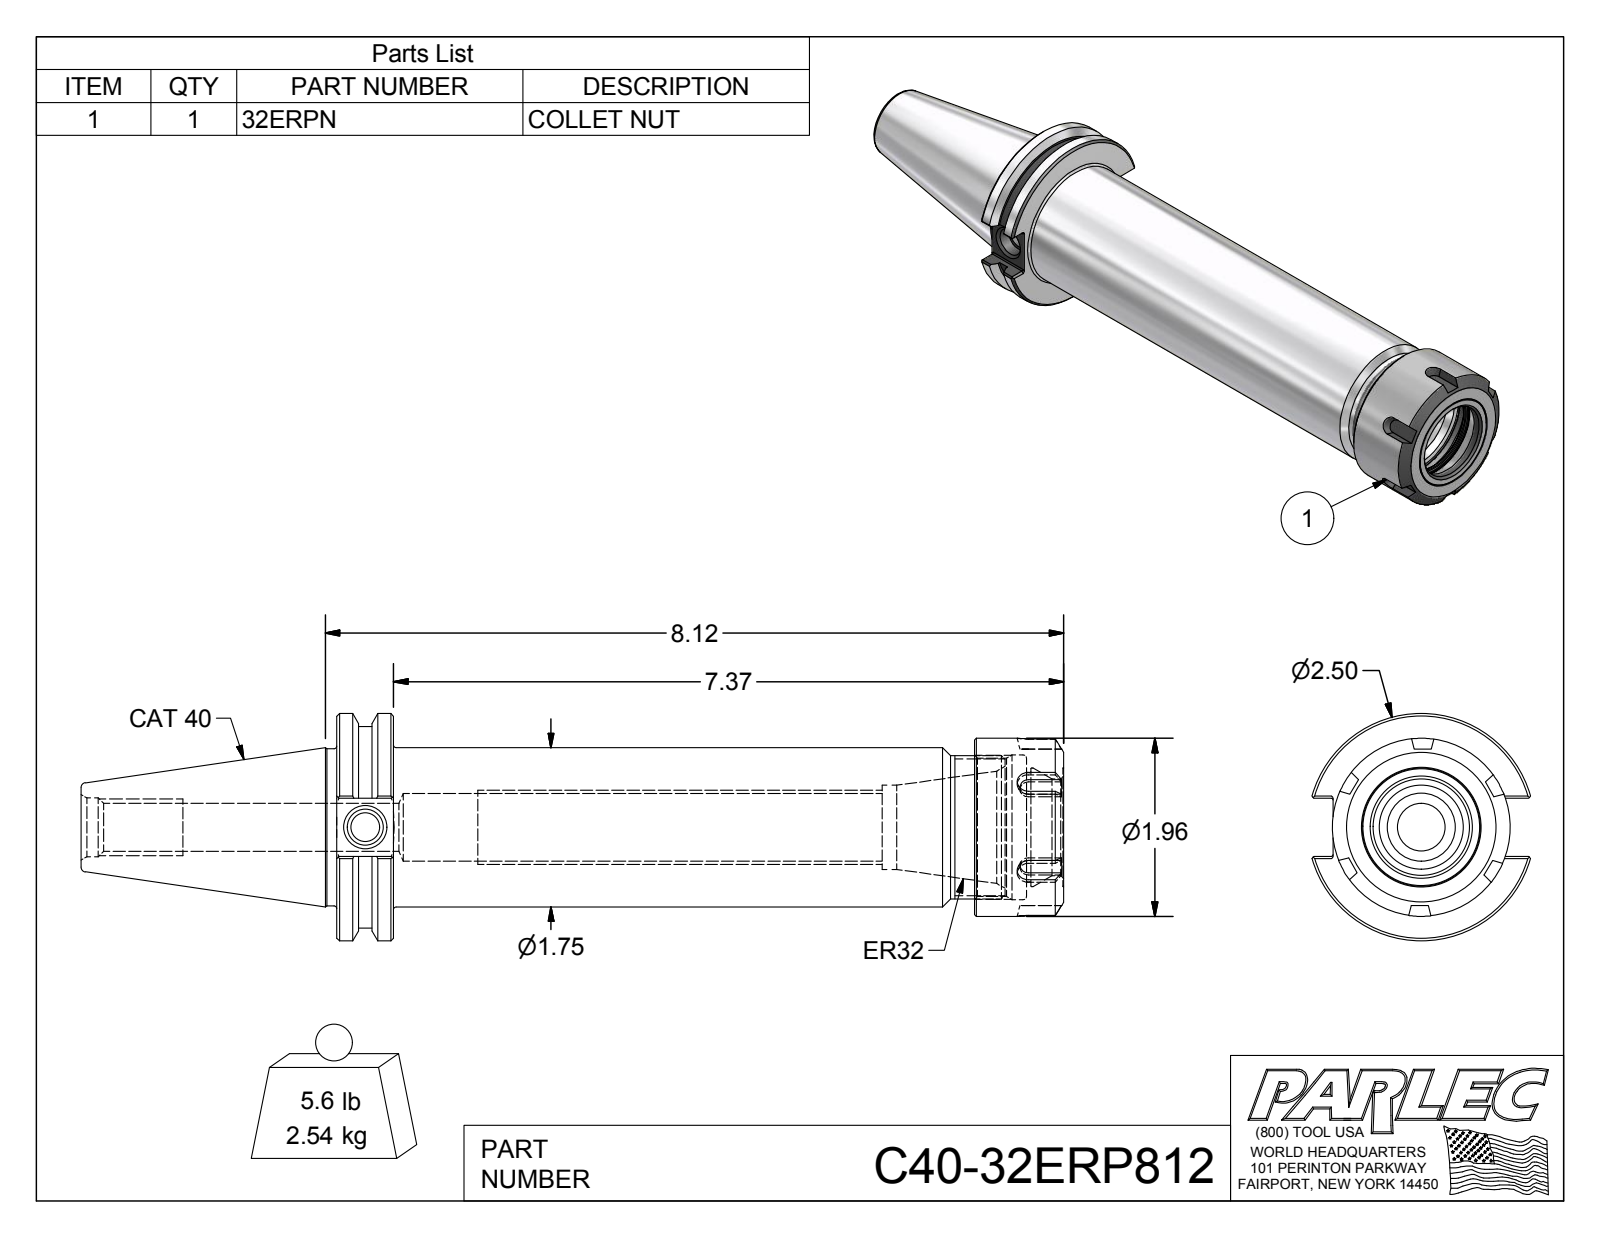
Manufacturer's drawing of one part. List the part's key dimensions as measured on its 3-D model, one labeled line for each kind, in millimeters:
Part name (STEP PRODUCT): C40-32ERP812; C40-32ER8-1; 32ERPN
STEP written by: Autodesk Inventor 2012 (AUTOMOTIVE_DESIGN)
Units: millimetres
Bodies: 2 solids, 129 faces (55 planar, 33 cylindrical, 41 other)
Overall size (bounding box): 274.5 × 63.5 × 61
Volume: 324 000 mm³ · Surface area: 63 450 mm²
Round holes (diameter × count): ⌀8 ×1, ⌀10.1 ×1, ⌀13.4 ×1, ⌀16.5 ×1, ⌀18.9 ×1, ⌀23.5 ×1, ⌀27 ×1, ⌀30.5 ×1, ⌀33.1 ×1, ⌀38.7 ×1, ⌀40.5 ×1
Round bosses / shafts (diameter × count): ⌀63.5 ×1, ⌀56.4 ×1, ⌀49.7 ×1, ⌀44.5 ×1, ⌀43.9 ×1, ⌀40 ×1
Partial cylindrical surfaces — rounded edges, fillets, slot ends (radius × count): R0.5 ×12
Main face-to-face distances: 15.9, 203.1, 187.2, 178.2, 162.4, 24.8, 192.7, 176.9, 14.5, 10.3
